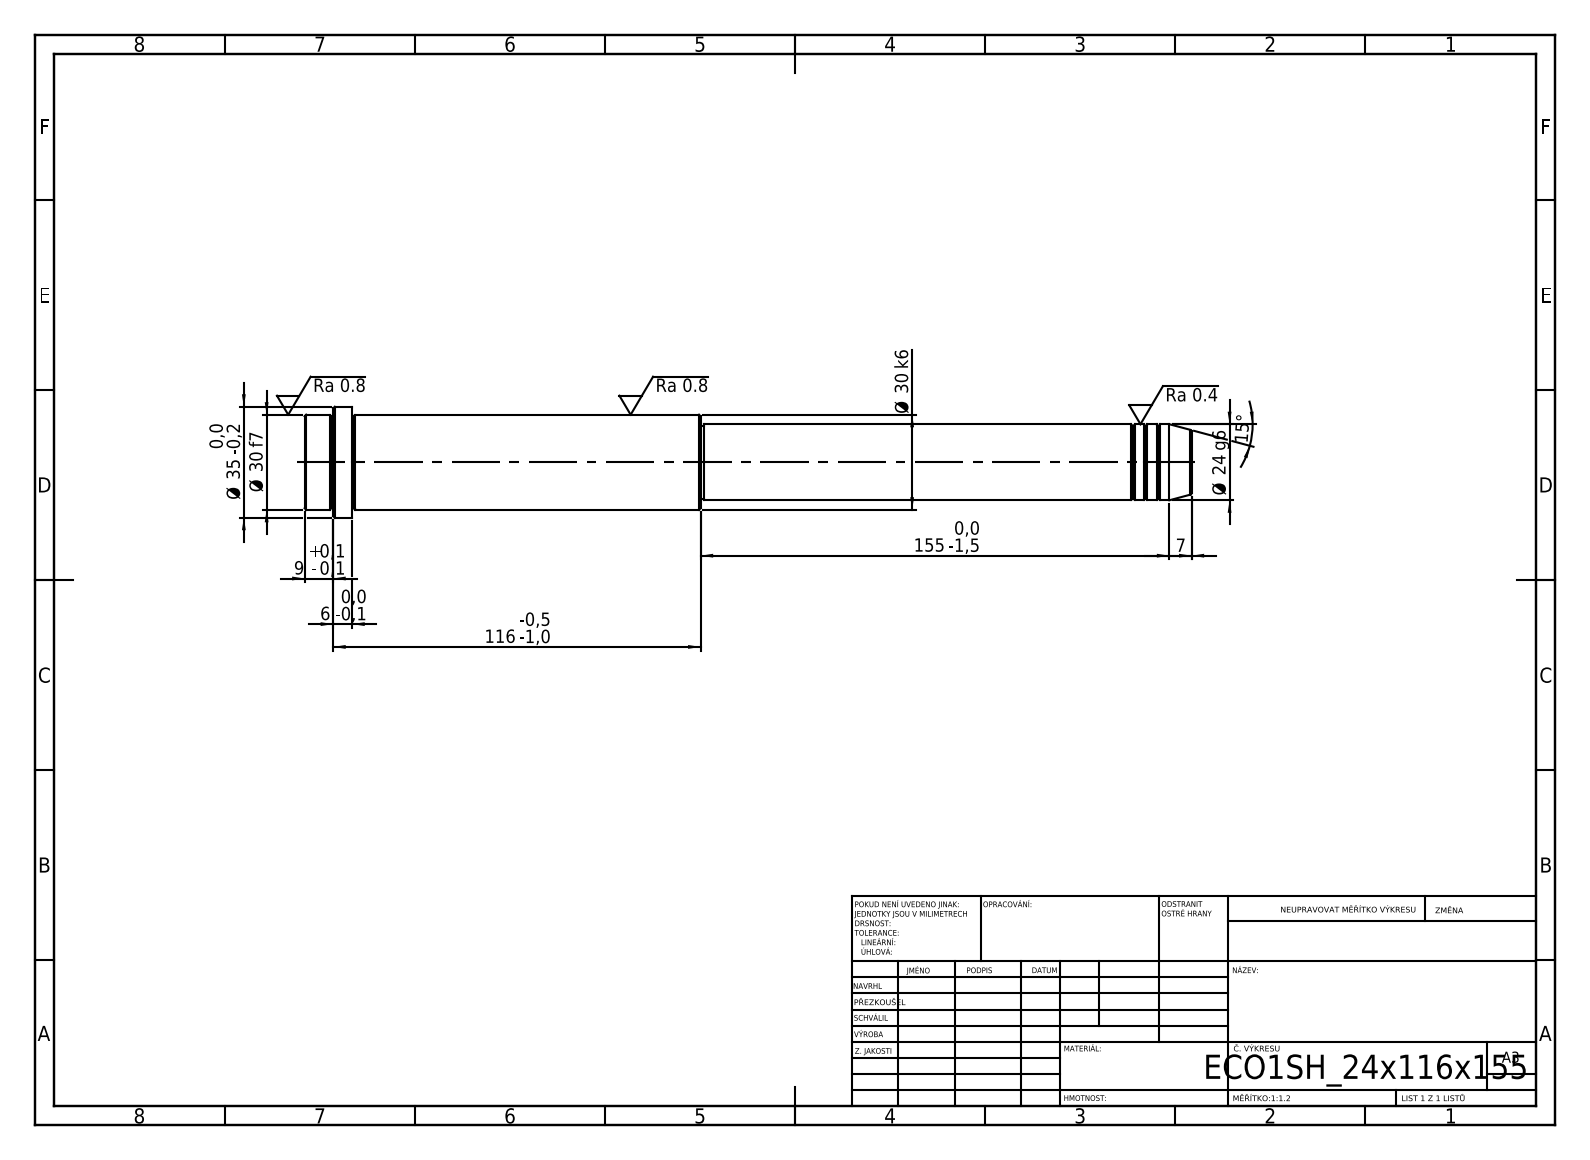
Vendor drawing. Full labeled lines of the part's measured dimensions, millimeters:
STEP written by: SolidWorks 2019 (CONFIG_CONTROL_DESIGN)
Units: millimetres
Bodies: 1 solid, 52 faces (6 planar, 16 cylindrical, 30 other)
Overall size (bounding box): 280 × 35 × 35
Volume: 159 304 mm³ · Surface area: 25 528 mm²
Round bosses / shafts (diameter × count): ⌀35 ×1, ⌀30 ×1, ⌀24 ×1, ⌀23 ×1
Main face-to-face distances: 280, 265, 15, 155, 110, 125, 271, 116, 6, 9
